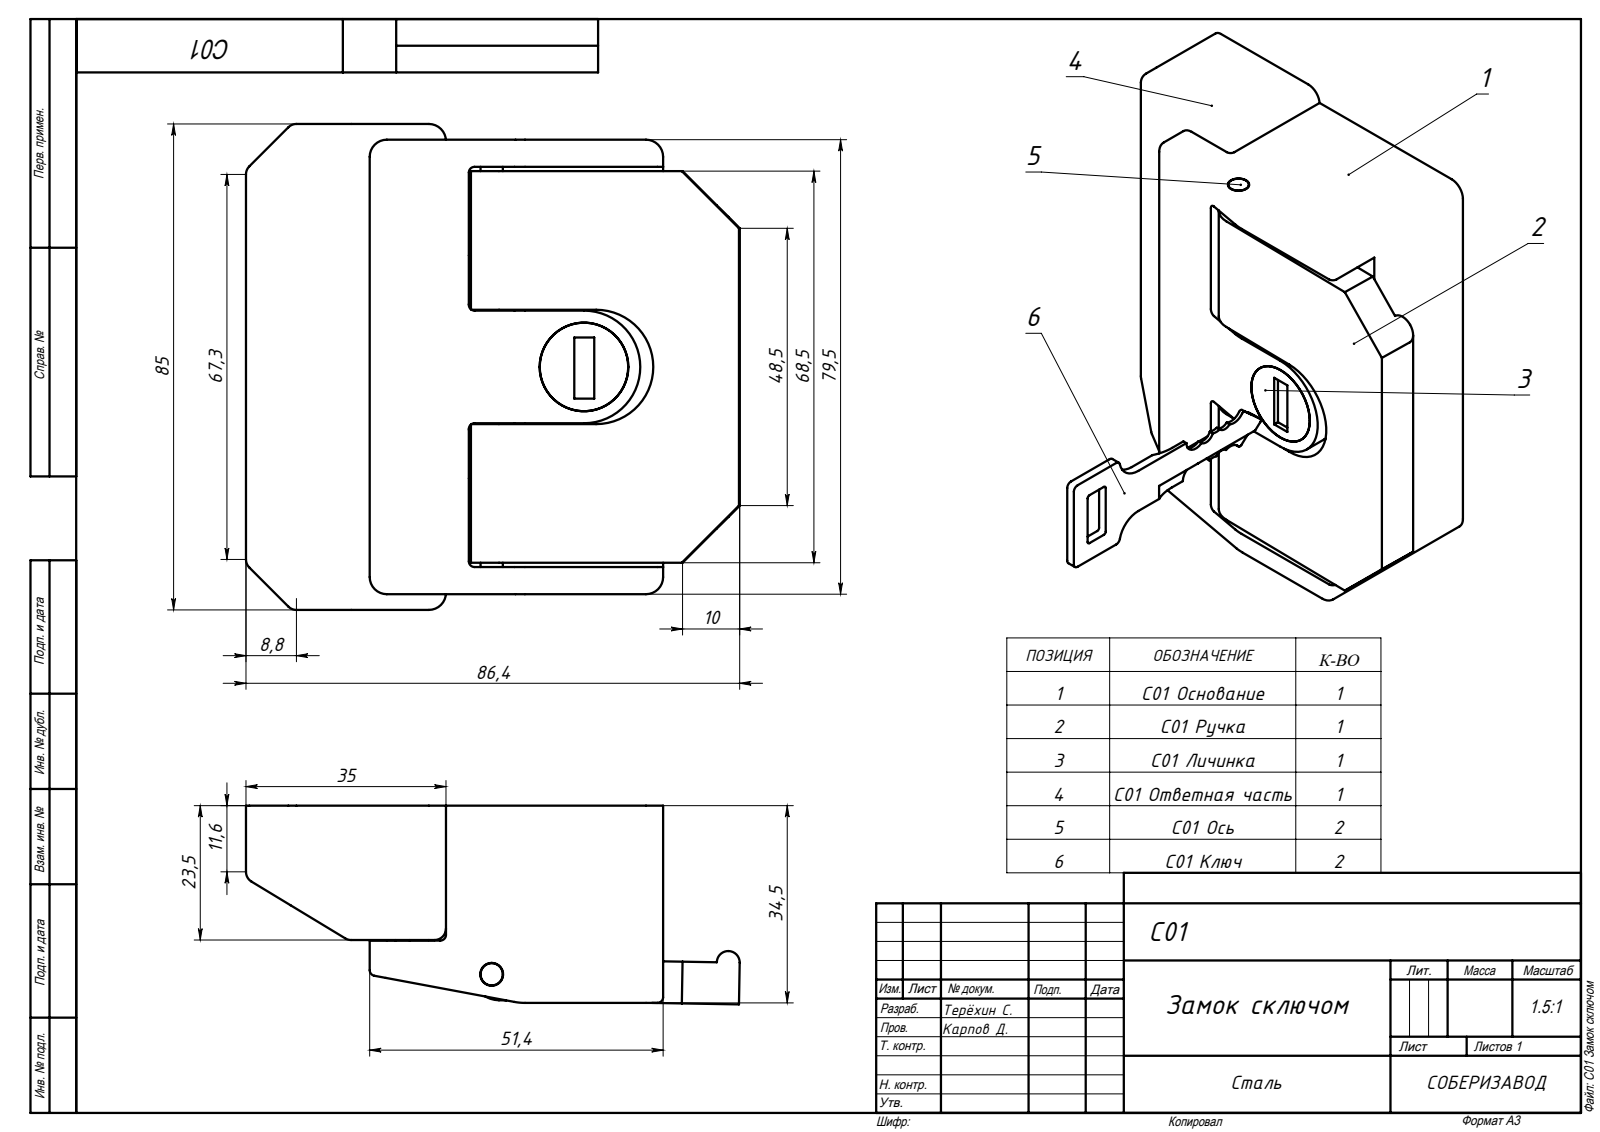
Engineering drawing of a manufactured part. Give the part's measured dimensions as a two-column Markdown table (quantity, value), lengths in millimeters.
| quantity | value |
| --- | --- |
| part name | С01 Ответная часть_00; С01 Личинка_00; C01 Ось_00; C01 Ручка_00 (+3 more) |
| STEP written by | SolidWorks 2020 (AUTOMOTIVE_DESIGN) |
| units | millimeters |
| bodies | 7 solids, 319 faces (186 planar, 115 cylindrical, 18 other) |
| overall size | 90.25 × 86.4 × 85 |
| volume | 106 096 mm³ |
| surface area | 56 536 mm² |
| round holes (diameter × count) | 4 × 1, 15.5 × 1 |
| round bosses / shafts (diameter × count) | 12 × 1, 3.9 × 1 |
| partial cylindrical surfaces (radius × count) | 1 × 19, 2 × 14, 0.5 × 8, 3 × 7, 10 × 4, 5 × 3, 1.25 × 2, 1.79 × 2 |
| main face-to-face distances | 2, 16, 23.5, 2.5, 5.5, 21.5, 0.5, 5, 18, 16.5 |
